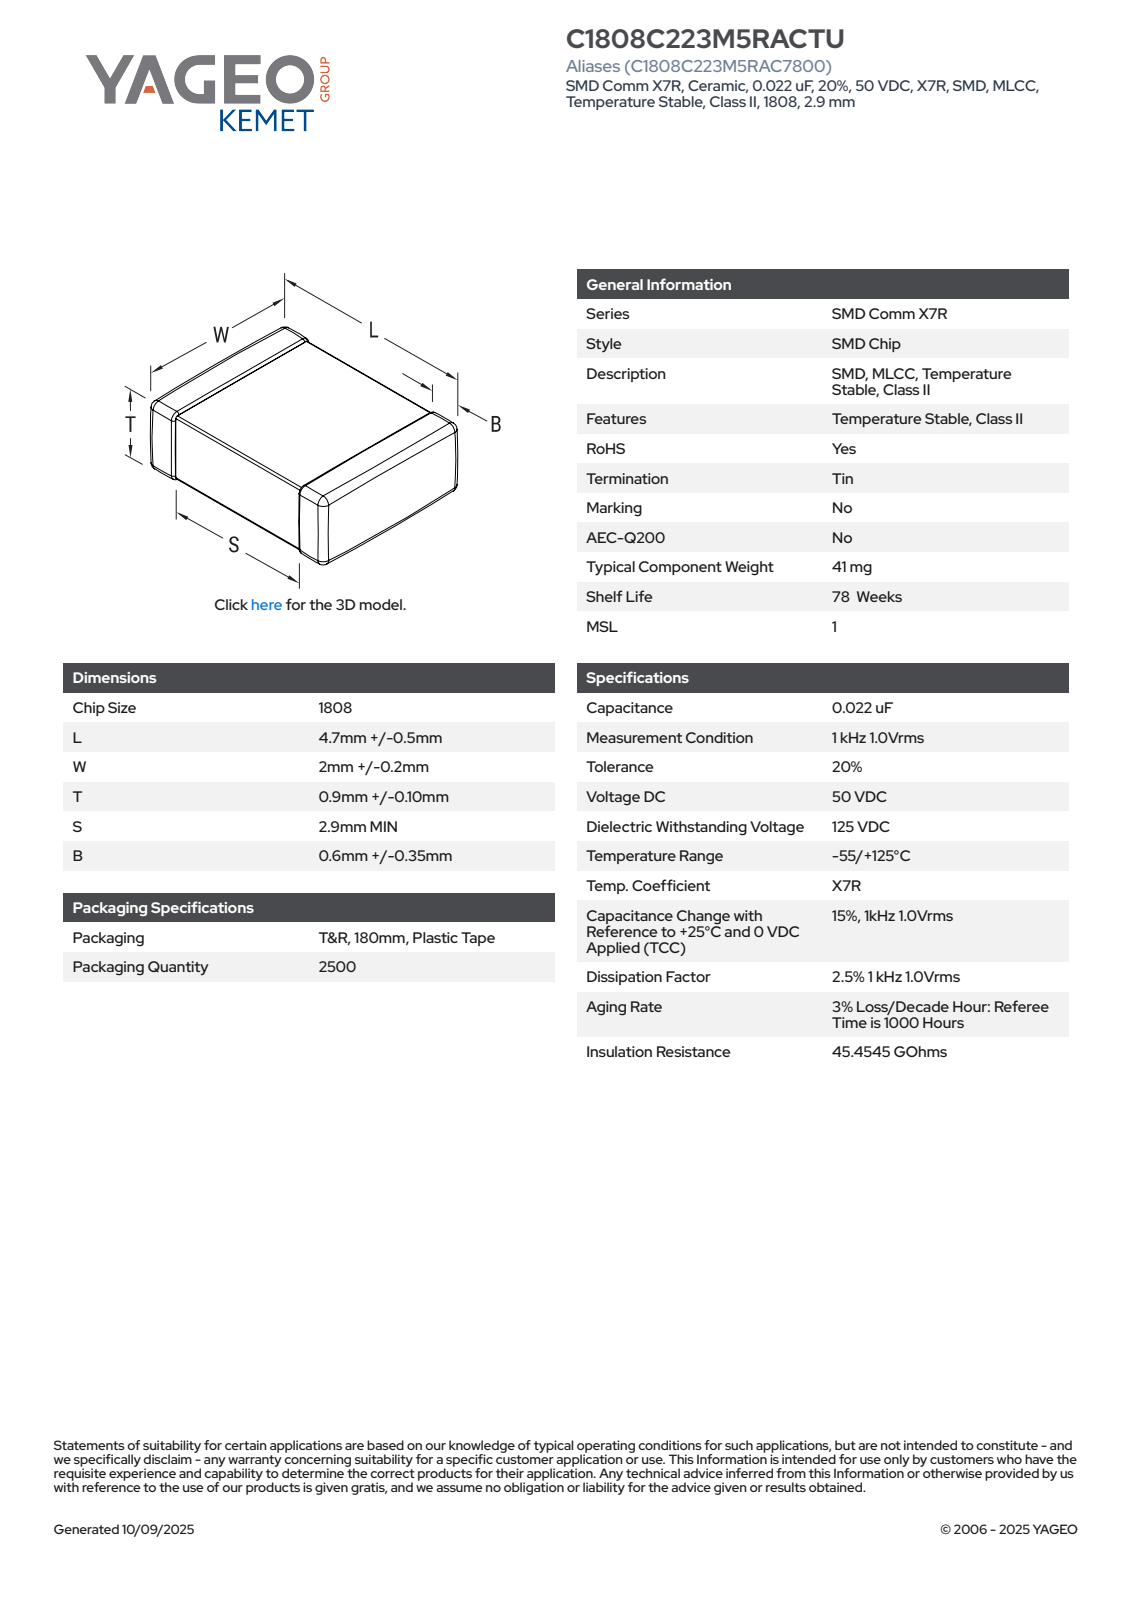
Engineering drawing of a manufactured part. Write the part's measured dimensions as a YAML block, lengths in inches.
part_name: "CCS_CCSTD_1808_L5.2W2.2T1B0.6"
step_written_by: "SolidWorks 2021 (AUTOMOTIVE_DESIGN)"
units: inches
bodies: {solids: 4, faces: 125, planar: 71, cylindrical: 38, other: 16}
overall_size: [0.205, 0.087, 0.039]
volume: 0.001
surface_area: 0.057
face_to_face_distances: [0.037, 0.035, 0.039, 0.085, 0.083, 0.205, 0.087, 0.036, 0.038, 0.013]
